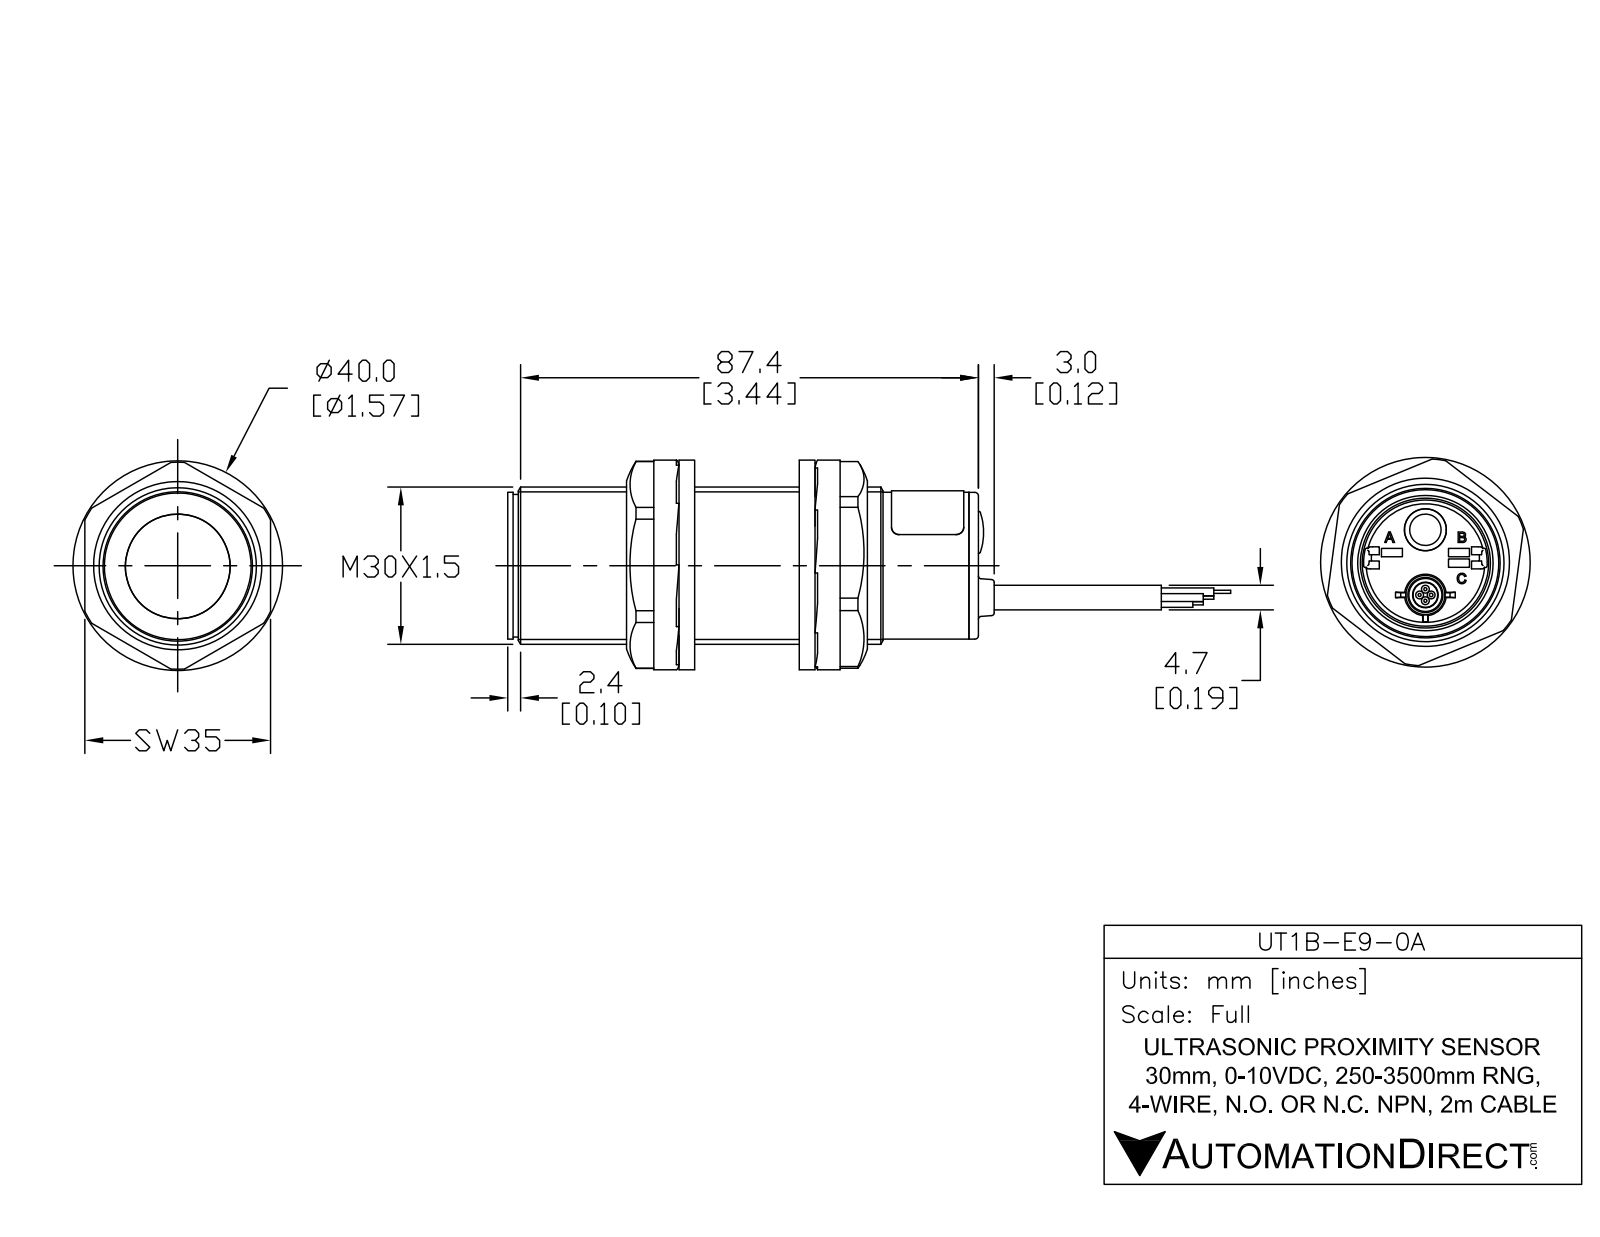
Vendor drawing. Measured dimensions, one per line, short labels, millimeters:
name: UT1B-E9-0A
written by: SolidWorks 2017 (AUTOMOTIVE_DESIGN)
unit: mm
bodies: 5 solids, 48 faces (13 planar, 18 cylindrical, 17 other)
size: 128 × 30 × 30
volume: 61 650 mm³; area: 12 810 mm²
holes: 1× ⌀4.7, 1× ⌀8, 1× ⌀23.5
bosses: 1× ⌀30, 1× ⌀28, 1× ⌀27.2
face distances: 86, 87.8, 1.8, 1, 87, 88.8, 1, 87, 88.8, 0.8
hole spacings: 6.1, 6.4, 12.4
